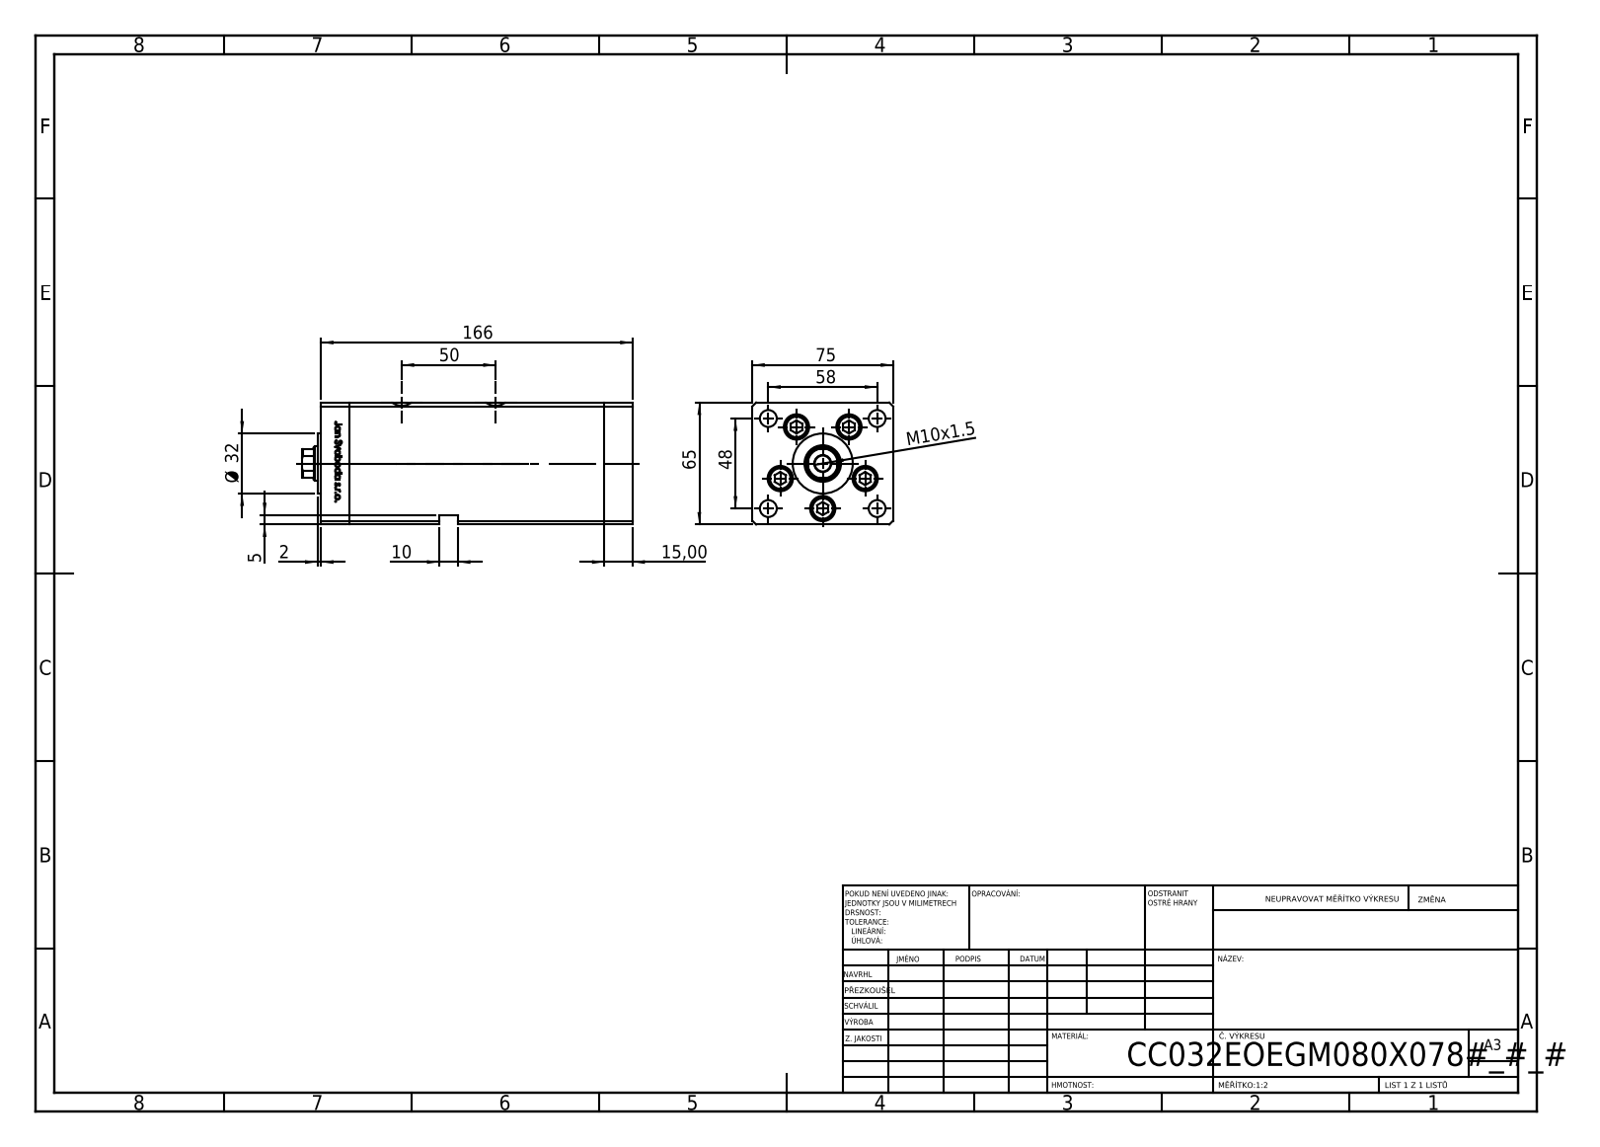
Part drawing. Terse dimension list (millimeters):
name: V220C_FRONT_E; V220C_VC_E; V220C_E MIDDLE; V220C BACK_E (+1 more)
written by: SolidWorks 2019 (CONFIG_CONTROL_DESIGN)
unit: mm
bodies: 13 solids, 1213 faces (473 planar, 165 cylindrical, 575 other)
size: 176 × 75 × 65
volume: 620 962 mm³; area: 137 442 mm²
holes: 9× ⌀9, 5× ⌀13.5, 4× ⌀10.5, 4× ⌀16.5, 2× ⌀2, 2× ⌀13.16, 1× ⌀8.5, 1× ⌀18, 1× ⌀19.5
bosses: 5× ⌀12.5, 5× ⌀8, 1× ⌀32
rounds: 2× R0.93, 1× R8.5
face distances: 75, 65, 15, 136, 151, 166, 28, 13, 54.5, 10.5
hole spacings: 24, 37.64, 58, 15.67, 17.22, 27.71, 28.83, 29
